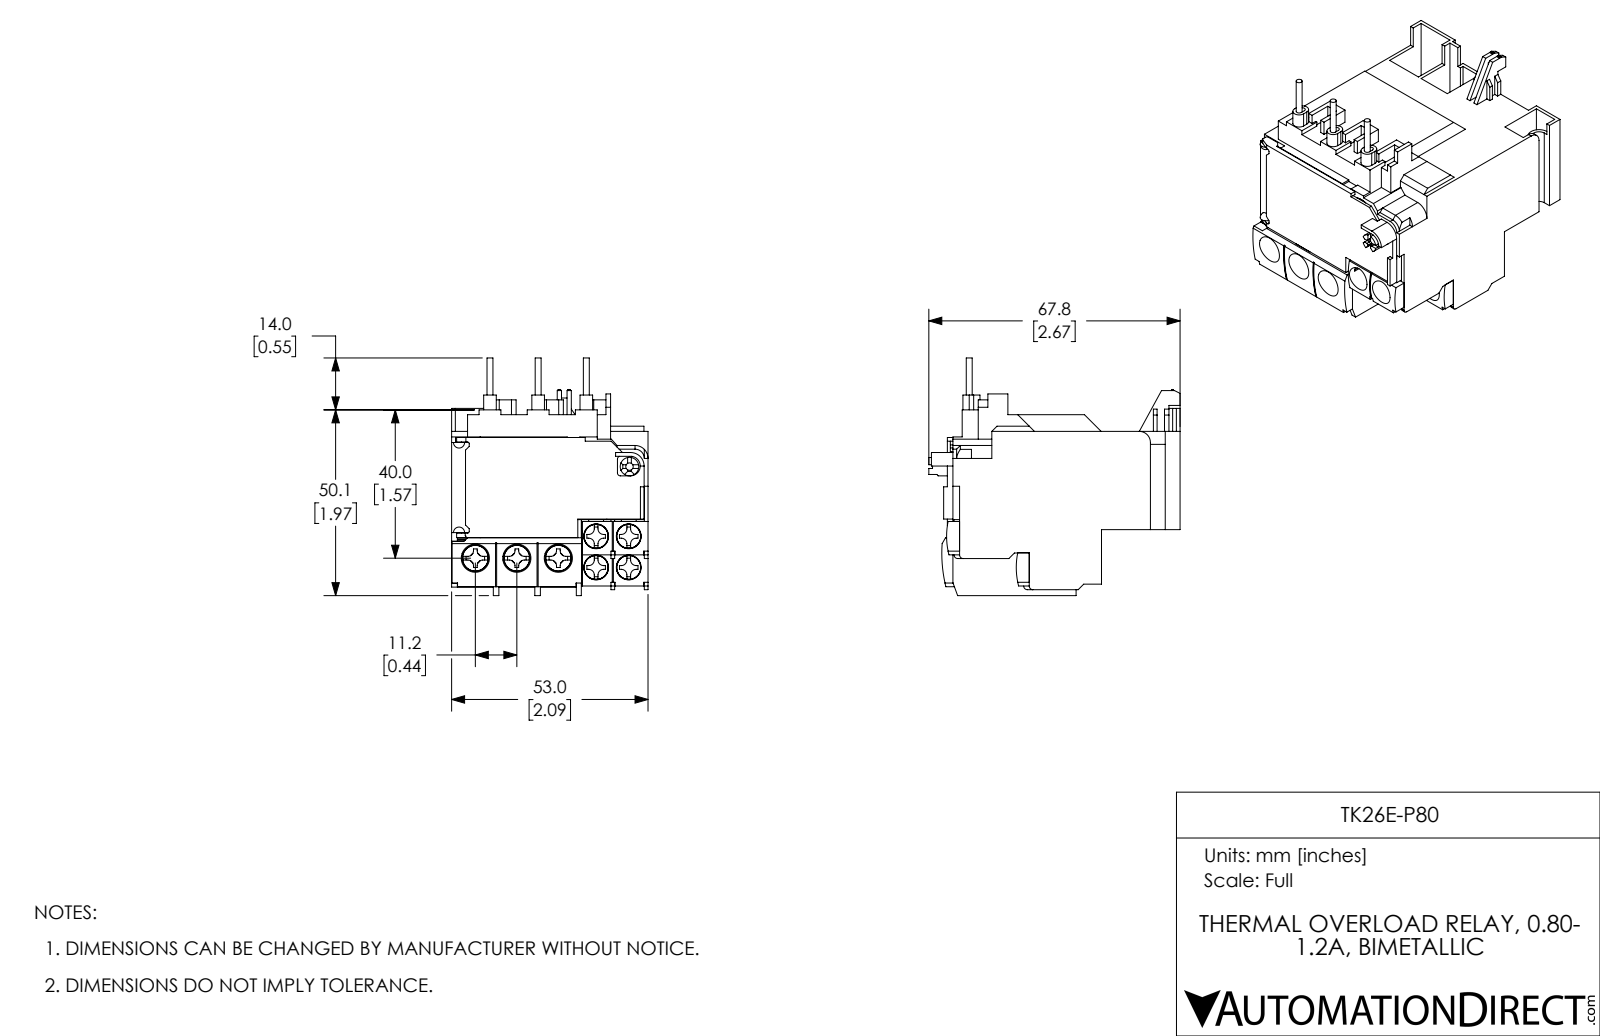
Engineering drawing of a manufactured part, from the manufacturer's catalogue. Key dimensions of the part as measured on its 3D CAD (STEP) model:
Part name (STEP PRODUCT): TK26E-P80
STEP written by: SolidWorks 2017 (AUTOMOTIVE_DESIGN)
Units: inches
Bodies: 38 solids, 1480 faces (1225 planar, 220 cylindrical, 35 other)
Overall size (bounding box): 2.669 × 2.524 × 2.087
Volume: 6.099 in³ · Surface area: 60.15 in²
Round holes (diameter × count): ⌀0.138 ×4, ⌀0.142 ×4, ⌀0.264 ×4, ⌀0.157 ×3, ⌀0.161 ×3, ⌀0.299 ×3, ⌀0.039 ×1, ⌀0.079 ×1, ⌀0.197 ×1, ⌀0.433 ×1
Round bosses / shafts (diameter × count): ⌀0.26 ×4, ⌀0.063 ×3, ⌀0.236 ×1
Partial cylindrical surfaces — rounded edges, fillets, slot ends (radius × count): R0.059 ×28, R0.039 ×8, R0.02 ×6, R0.067 ×6, R0.031 ×5, R0.047 ×4, R0.171 ×4, R0.189 ×3
Main face-to-face distances: 0.039, 0.354, 0.059, 0.472, 2.087, 0.079, 0.394, 0.433, 0.343, 0.028
Hole centre spacings: 0.331, 0.346, 0.441, 0.479, 0.376, 0.413, 0.464, 0.74
